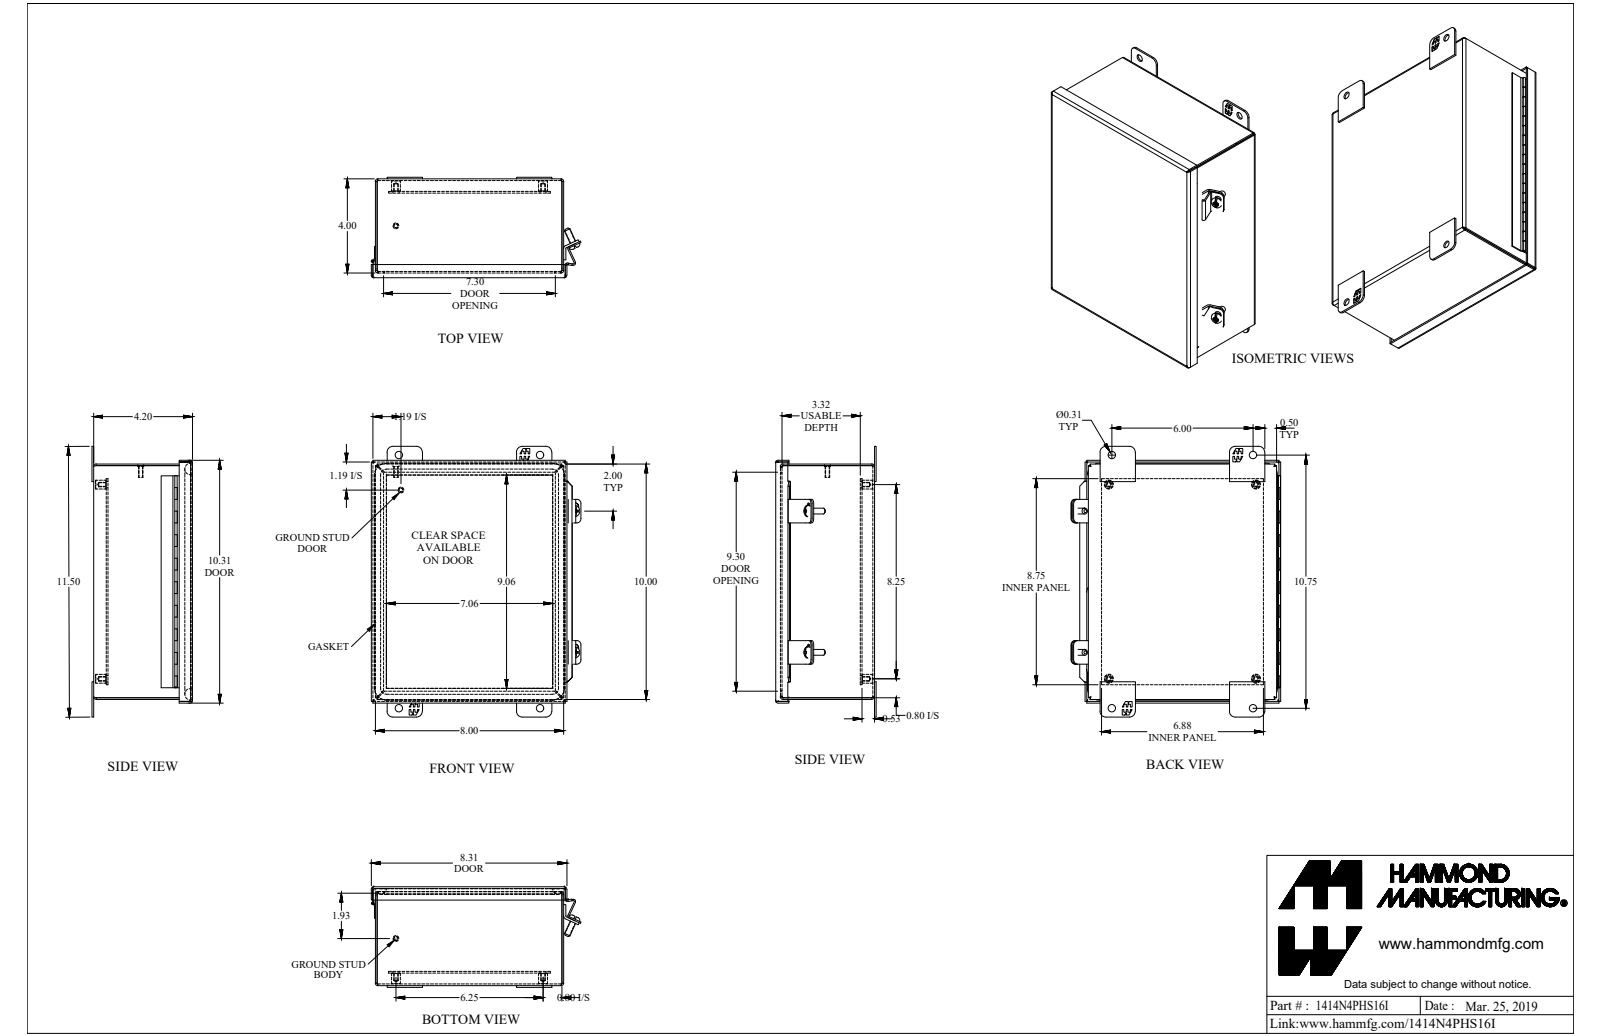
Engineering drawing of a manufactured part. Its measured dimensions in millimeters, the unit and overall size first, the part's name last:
Units: millimetres
Overall size (bounding box): 292.1 × 226.1 × 108.4
Round holes (diameter × count): ⌀4 ×4, ⌀6.7 ×4, ⌀8 ×4, ⌀5.4 ×2, ⌀1.3 ×1
Round bosses / shafts (diameter × count): ⌀9.5 ×4, ⌀6.4 ×4, ⌀12.2 ×2, ⌀4.8 ×2, ⌀2.5 ×1, ⌀1.1 ×1
Partial cylindrical surfaces — rounded edges, fillets, slot ends (radius × count): R6.4 ×24, R0.9 ×8, R2.7 ×8, R4.8 ×8, R2 ×4, R3 ×4, R3.6 ×4, R12.7 ×4
Main face-to-face distances: 1.8, 13.5, 2.1, 104.8, 106.6, 104.5, 91.3, 102.7, 201.4, 15.3
Hole centre spacings: 31.9, 158.8, 241.3, 262.9, 287.1, 152.4, 158.8, 158.8
Volume: 559 900 mm³ · Surface area: 604 100 mm²
Bodies: 21 solids, 677 faces (443 planar, 176 cylindrical, 58 other)
Part name (STEP PRODUCT): 1414N4PHS16I
STEP written by: SolidWorks 2018 (AUTOMOTIVE_DESIGN)
